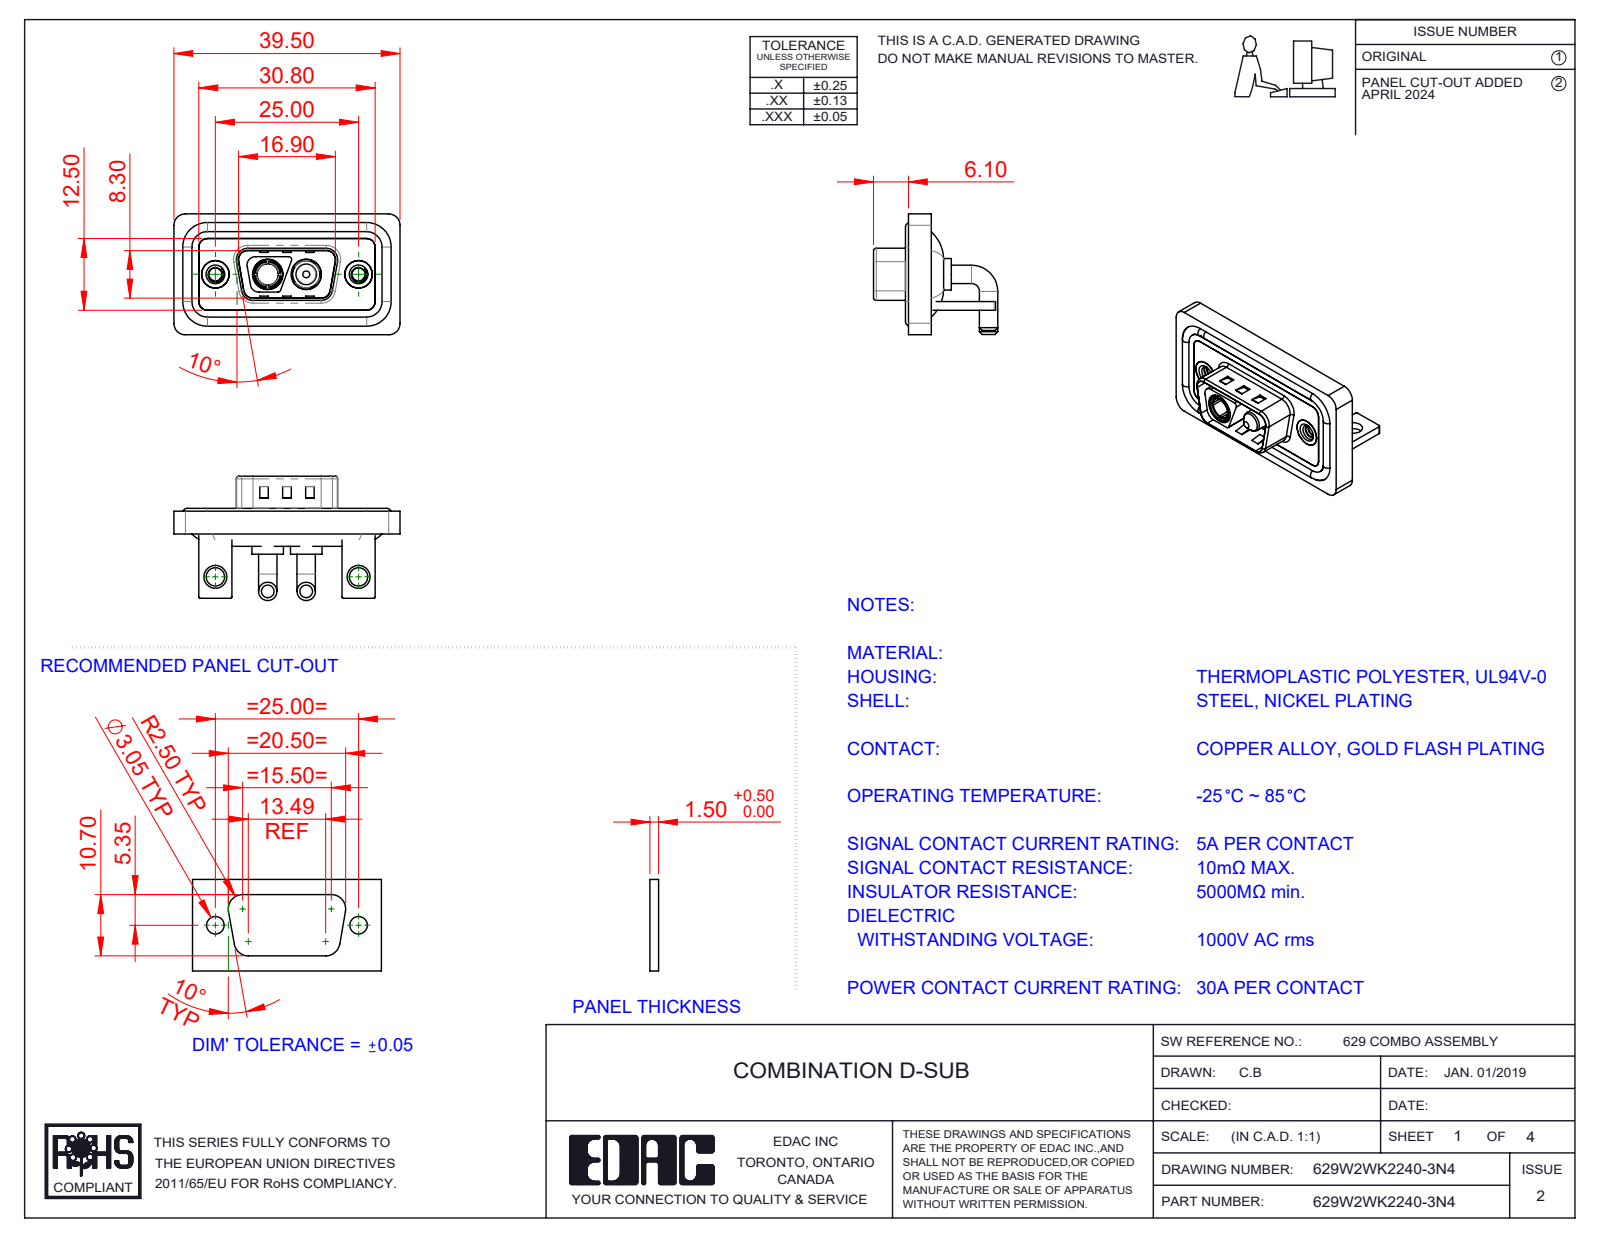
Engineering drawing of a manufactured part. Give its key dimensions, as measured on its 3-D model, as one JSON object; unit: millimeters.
{"part_name": "629W2WK2140-3N4; 629Combo Waterproof Housing_09 Contacts; 629Combo Shell Rear_09 Contacts; 629Combo Shell Front_09 Contacts (+5 more)", "step_written_by": "SolidWorks 2023 (CONFIG_CONTROL_DESIGN)", "units": "millimeters", "bodies": {"solids": 13, "faces": 582, "planar": 209, "cylindrical": 249, "other": 124}, "overall_size": [39.5, 21.7, 21.1], "volume_mm3": 5017, "surface_area_mm2": 8157, "round_holes": [[2.26, 2], [3.2, 2], [4, 2], [4.8, 2], [4.85, 2], [5, 2], [5.3, 2], [3.7, 1]], "round_bosses_or_shafts": [[3.2, 4], [1.6, 4], [5.5, 2], [5.2, 2], [4.9, 2], [4.75, 2], [3.75, 2], [4.96, 1]], "partial_cylinders_radius": [[1.5, 20], [2, 19], [0.25, 16], [0.5, 11], [1.6, 8], [0.6, 4], [0.65, 4], [0.9, 4]], "face_to_face_distances": [0.4, 1.5, 2.9, 0.8, 1.1, 1.2, 2.1, 1.6, 3.7, 2.5], "hole_center_spacings": [9.14, 15.86, 25, 6.72]}
